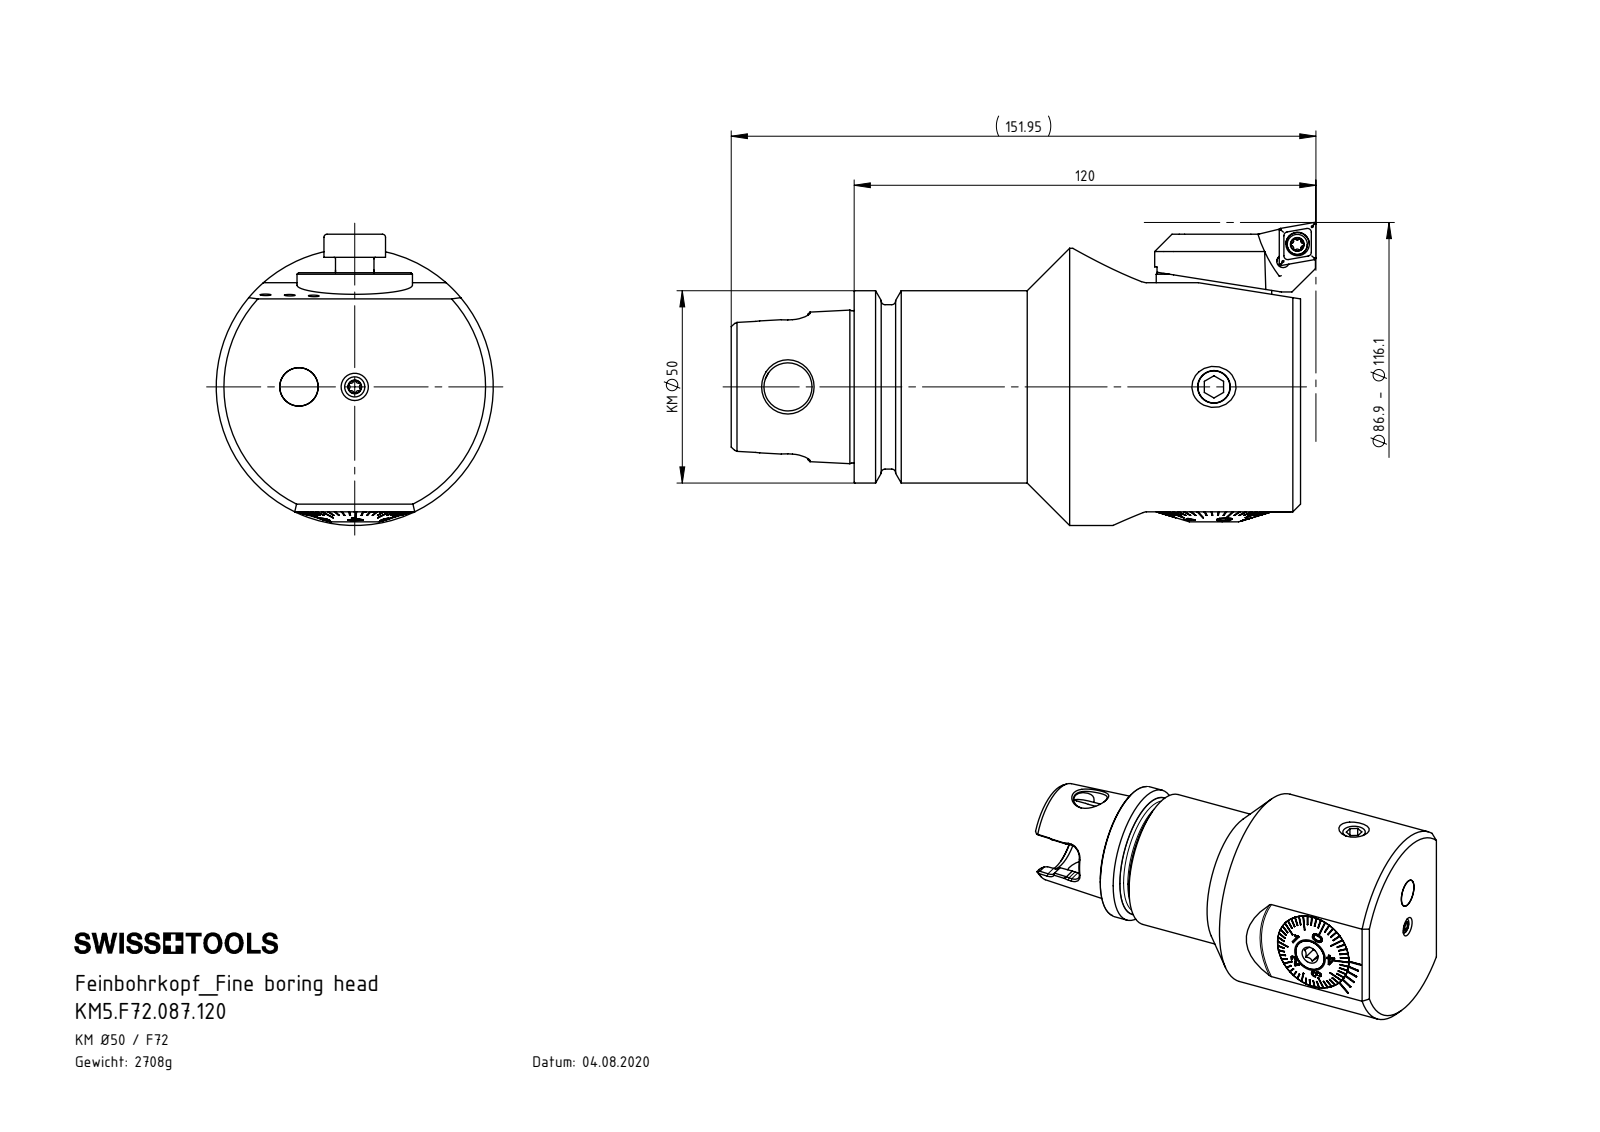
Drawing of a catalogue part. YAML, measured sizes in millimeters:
part_name: "F72-BG1.DA3.030_A; Klebstoff D10; DIN 7984 - M10 x 16; A55-BG2.013.005_C (+8 more)"
step_written_by: "SolidWorks 2017 (AUTOMOTIVE_DESIGN)"
units: millimeters
bodies: {solids: 13, faces: 635, planar: 321, cylindrical: 99, other: 215}
overall_size: [147.95, 75.66, 72]
volume: 347826
surface_area: 62904
round_holes:
  - {diameter: 2.5, count: 3}
  - {diameter: 4.2, count: 3}
  - {diameter: 8.5, count: 3}
  - {diameter: 3.3, count: 2}
  - {diameter: 5, count: 1}
  - {diameter: 8, count: 1}
  - {diameter: 10, count: 1}
  - {diameter: 11.4, count: 1}
  - {diameter: 12, count: 1}
  - {diameter: 12.4, count: 1}
  - {diameter: 12.5, count: 1}
  - {diameter: 13, count: 1}
round_bosses_or_shafts:
  - {diameter: 10, count: 2}
  - {diameter: 72, count: 1}
  - {diameter: 49.95, count: 1}
  - {diameter: 42.7, count: 1}
  - {diameter: 30, count: 1}
  - {diameter: 29.98, count: 1}
  - {diameter: 29.9, count: 1}
  - {diameter: 25, count: 1}
partial_cylinders:
  - {radius: 0.34, count: 6}
  - {radius: 0.59, count: 6}
  - {radius: 2.5, count: 6}
  - {radius: 4, count: 6}
  - {radius: 2, count: 4}
  - {radius: 3.2, count: 3}
  - {radius: 0.5, count: 2}
  - {radius: 6.04, count: 2}
face_to_face_distances: [53.01, 2.6, 62.11, 59.51, 6.5, 2.5, 58.31, 5.3, 1.2, 55.81]
hole_center_spacings: [14.5, 17.97, 19.81, 29, 110.7, 125.04]
